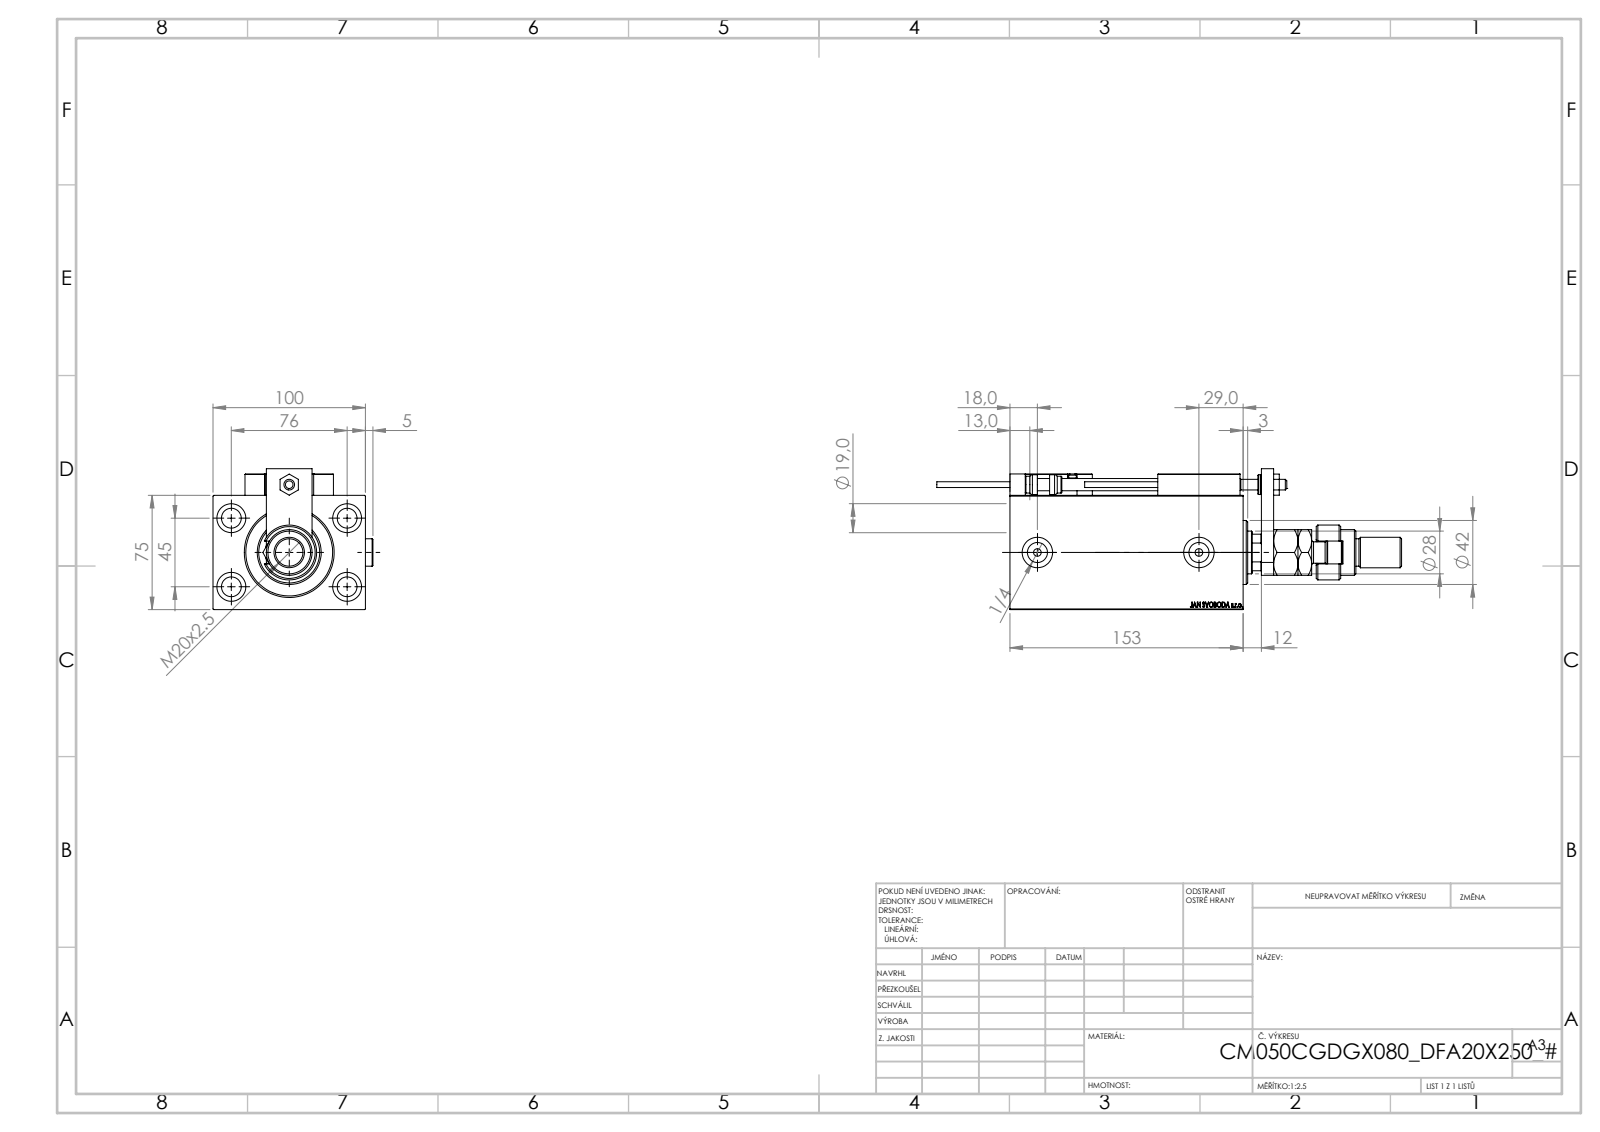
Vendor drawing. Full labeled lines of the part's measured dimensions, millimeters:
Part name (STEP PRODUCT): MFA; SWITCH DIM B,W; Zatka_OIL_PORT; TYC_L79 (+7 more)
STEP written by: SolidWorks 2019 (CONFIG_CONTROL_DESIGN)
Units: millimetres
Bodies: 27 solids, 1424 faces (623 planar, 219 cylindrical, 582 other)
Overall size (bounding box): 305 × 104.9 × 92.5
Volume: 1 046 000 mm³ · Surface area: 191 503 mm²
Round holes (diameter × count): ⌀8 ×5, ⌀3.2 ×4, ⌀4 ×4, ⌀5 ×4, ⌀13 ×4, ⌀19 ×4, ⌀20 ×3, ⌀13.16 ×2, ⌀7 ×1, ⌀18.5 ×1, ⌀28 ×1, ⌀31.5 ×1
Round bosses / shafts (diameter × count): ⌀18 ×3, ⌀5 ×2, ⌀3.8 ×2, ⌀42 ×1, ⌀36 ×1, ⌀30 ×1, ⌀22 ×1, ⌀14 ×1
Partial cylindrical surfaces — rounded edges, fillets, slot ends (radius × count): R0.3 ×30, R3 ×2, R7.5 ×1, R12 ×1, R13.5 ×1
Main face-to-face distances: 75, 100, 14, 153, 12, 139, 20, 8, 24, 25
Hole centre spacings: 44.16, 11.37, 20, 29.59, 29.69, 36.06, 42.19, 43.91
